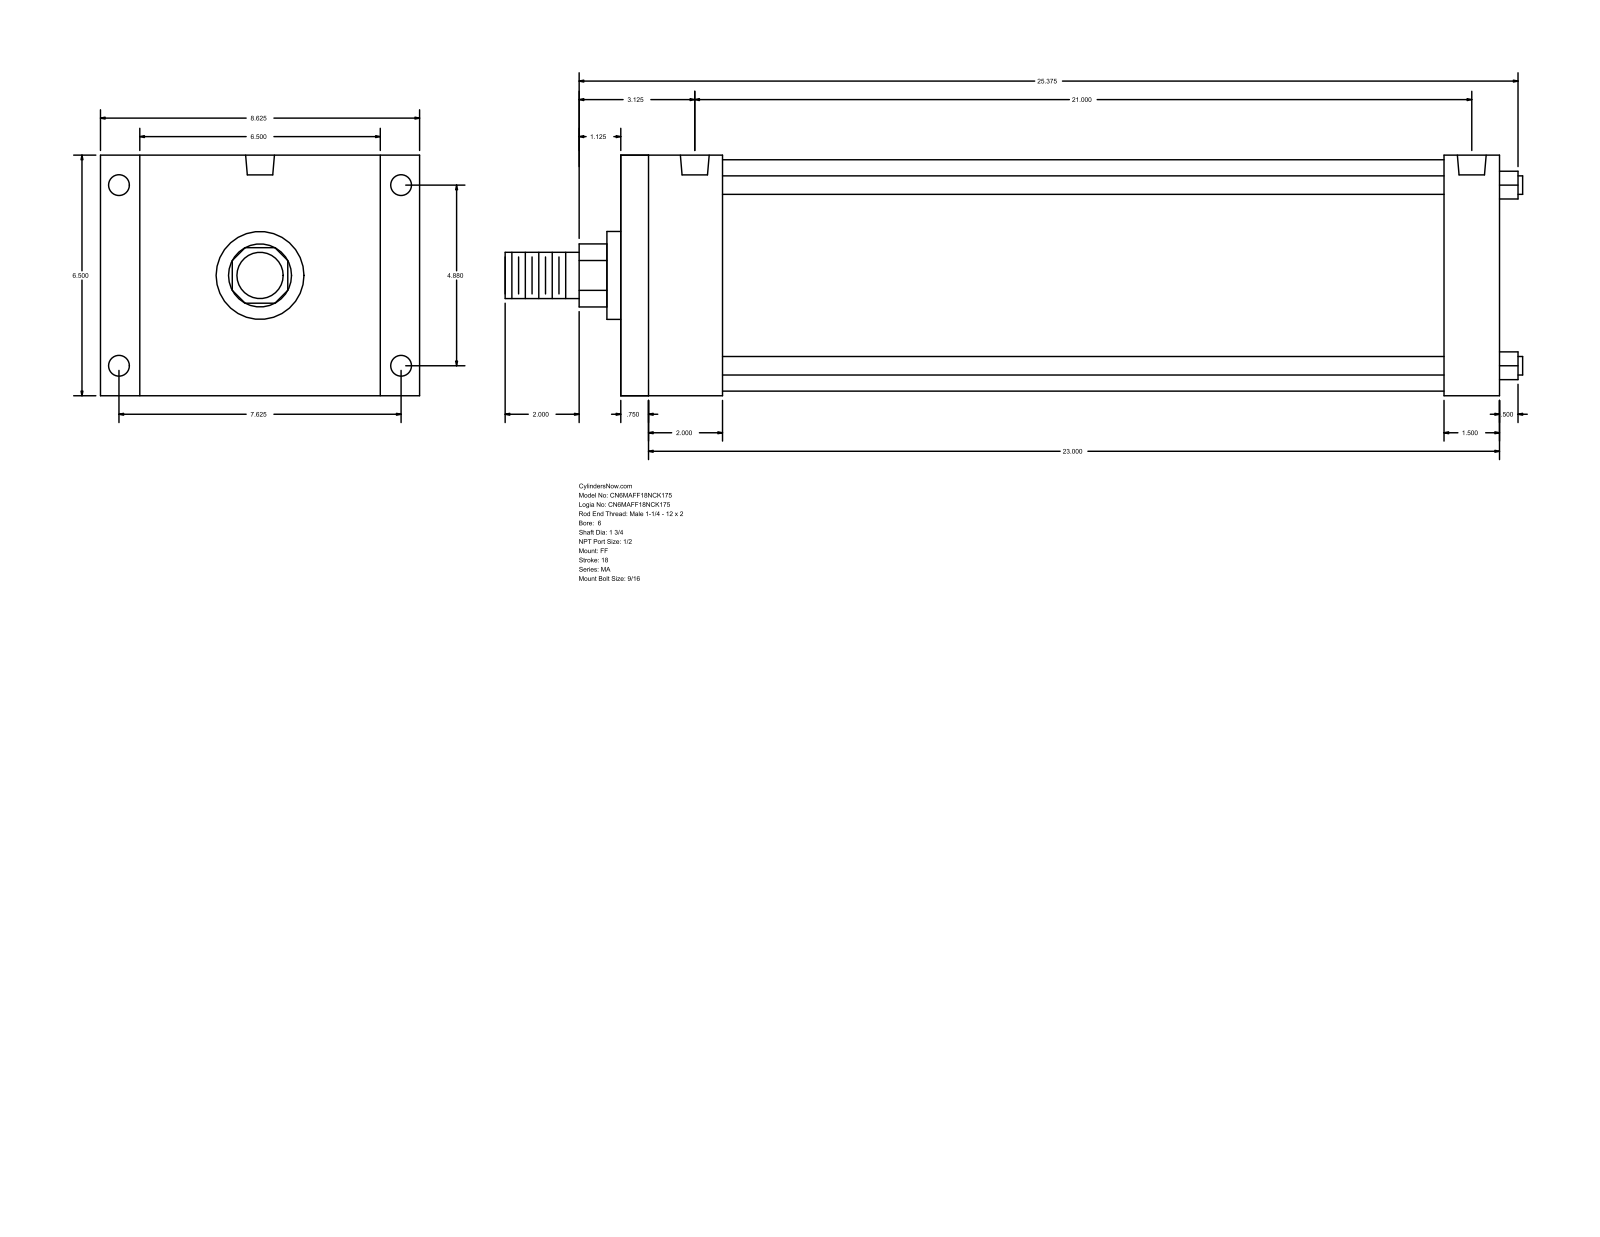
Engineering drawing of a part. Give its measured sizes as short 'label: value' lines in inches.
name: MA_FF__0600_1.75
written by: GSSL Pune (CONFIG_CONTROL_DESIGN)
unit: in
bodies: 0 solids, 92 faces (64 planar, 28 cylindrical, 0 other)
size: 27.5 × 8.625 × 6.5
holes: 4× ⌀0.563, 4× ⌀0.687, 2× ⌀0.778
bosses: 4× ⌀0.5, 1× ⌀6.25, 1× ⌀2.375, 1× ⌀1.75, 1× ⌀1.25
rounds: 1× R0.852
face distances: 6.5, 23.75, 0.75, 23, 2.75, 1.5, 2, 21, 22.25, 21.5
hole spacings: 4.88, 7.625, 9.053, 21
